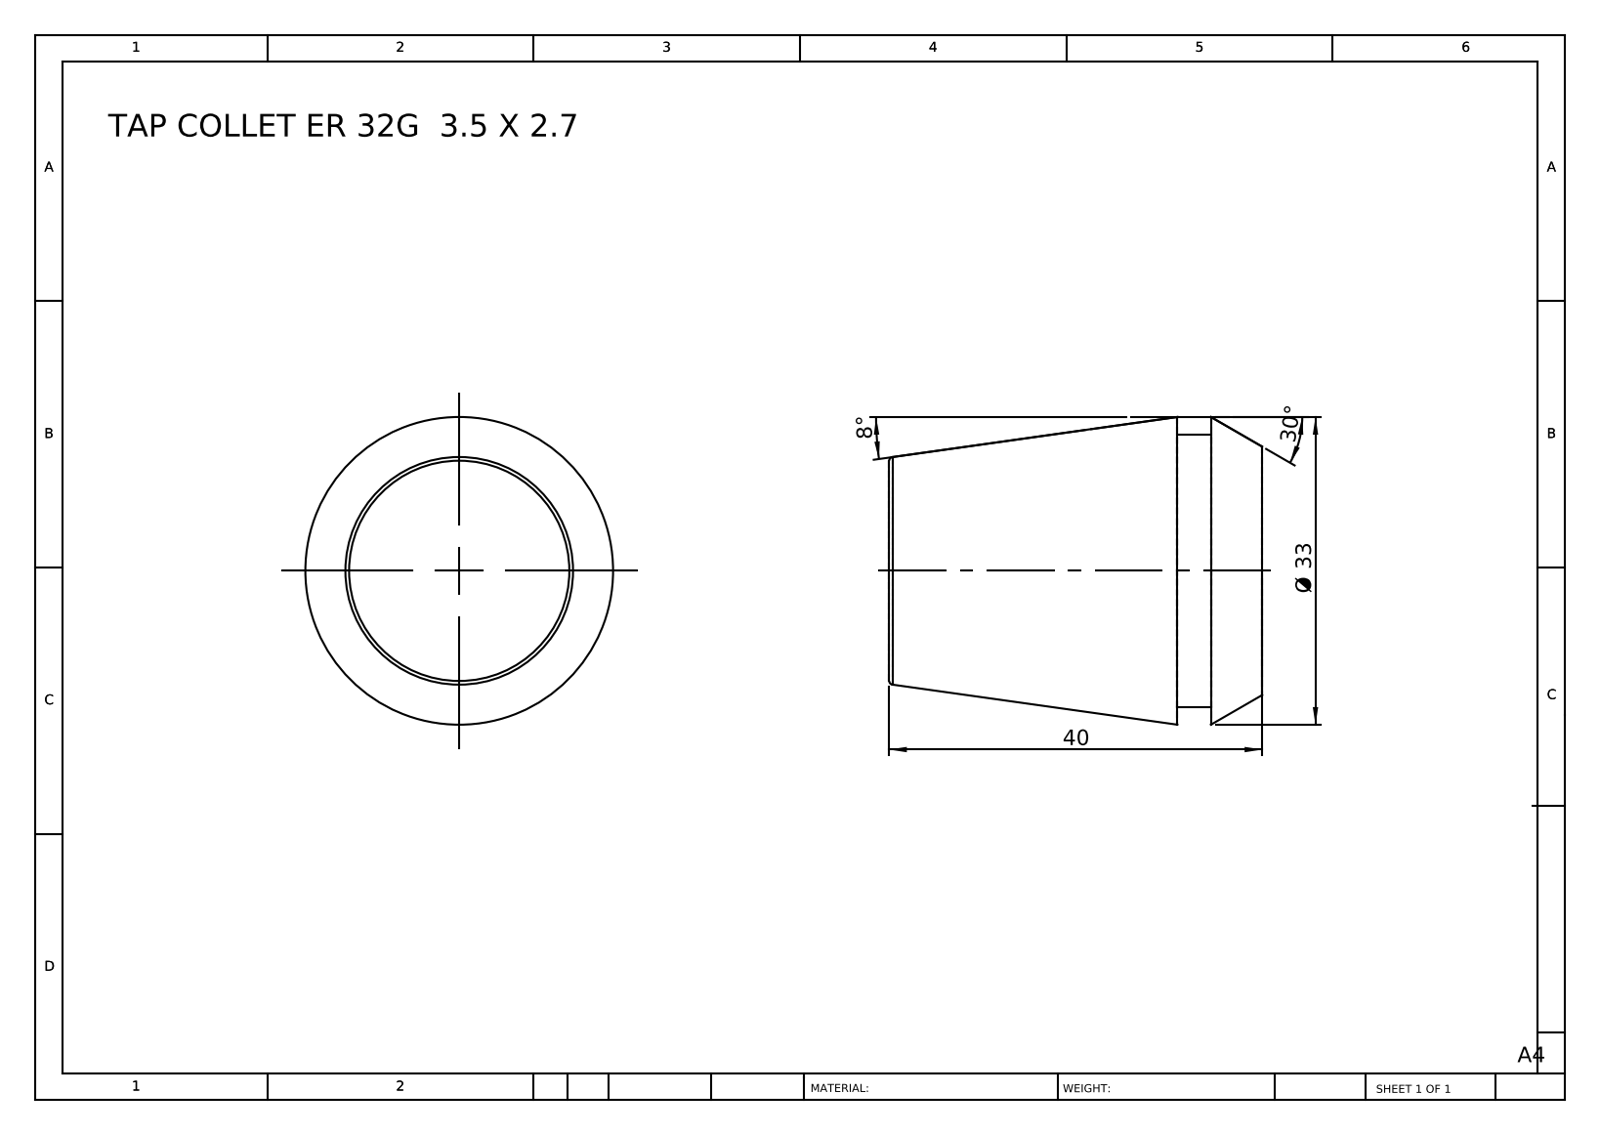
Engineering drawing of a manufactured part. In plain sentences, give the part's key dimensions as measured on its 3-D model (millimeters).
The part is named "TAP COLLET ER 32G 3.5 X 2.7". Its 3-D file was written by "SolidWorks 2014 (CONFIG_CONTROL_DESIGN)". It is 1 solid with 12 faces: 4 planar, 2 cylindrical and 6 other. Overall it measures 40 by 33 by 33 millimeters. Its volume is 26 350 cubic millimeters and its surface area 5 119 square millimeters. Round bosses or shafts: 1 of diameter 29.2. The main face-to-face distances are 40, 9.1, 30.9, 5.5, 3.6, 34.5.
